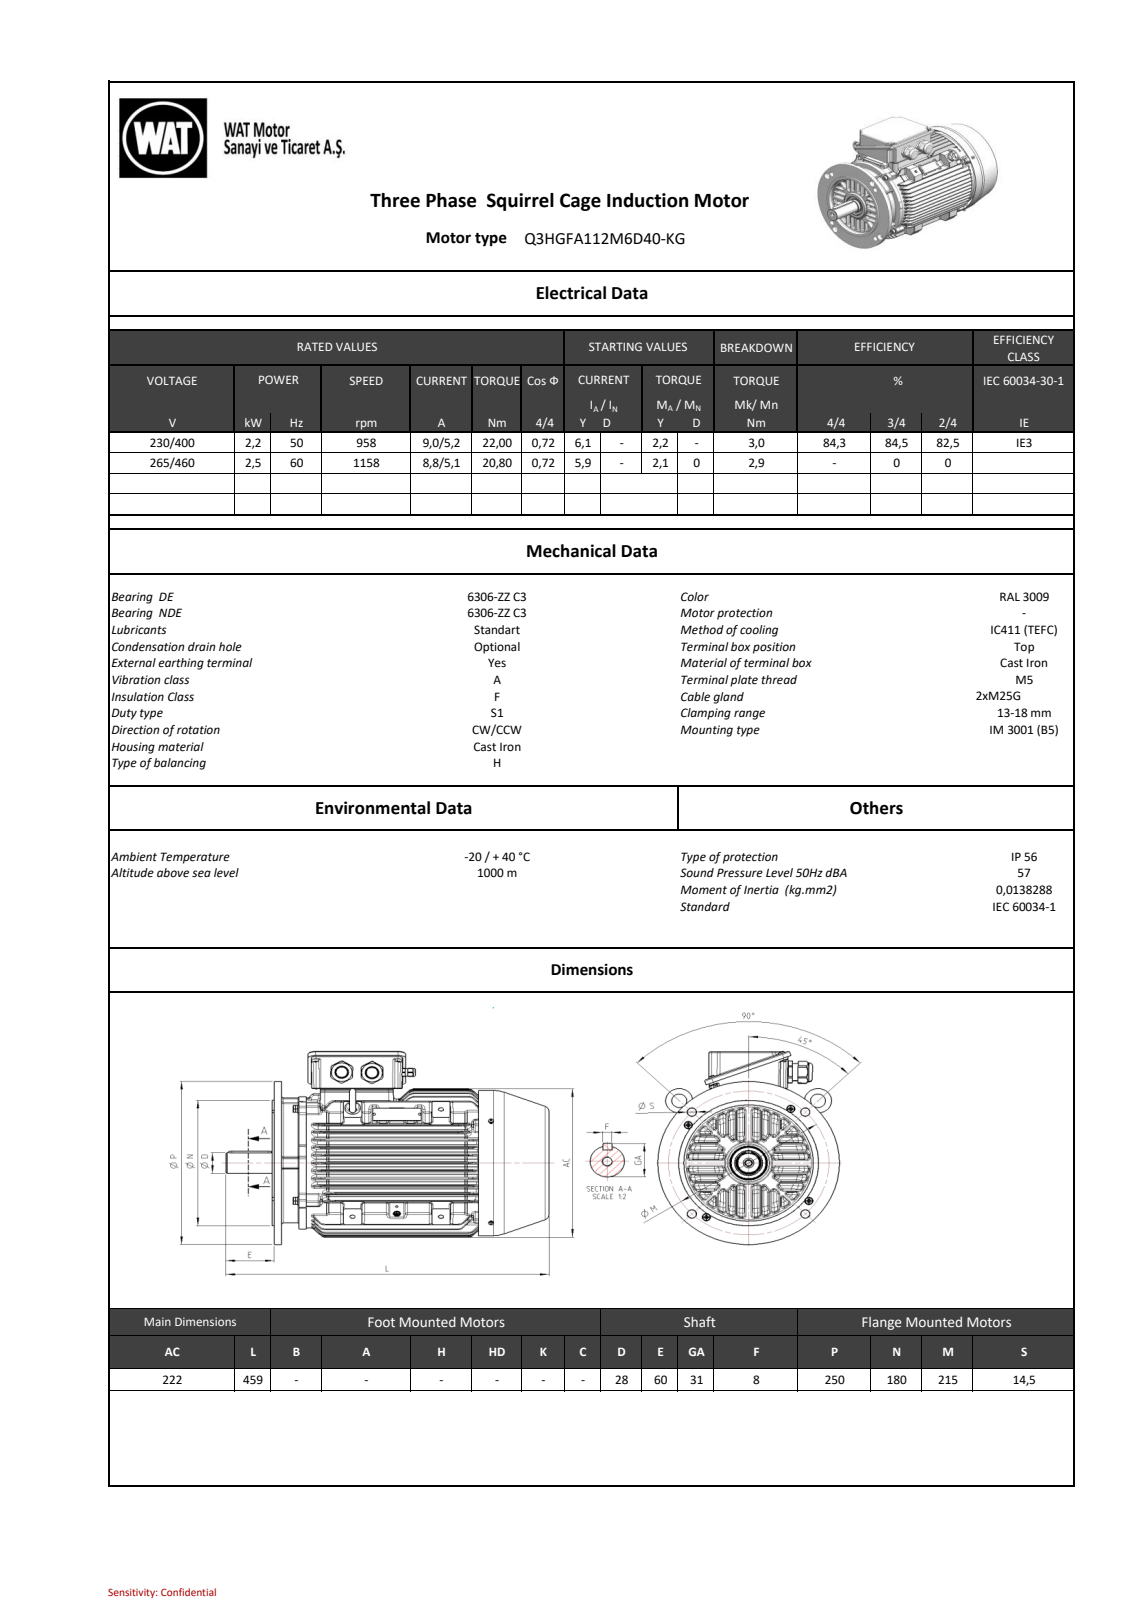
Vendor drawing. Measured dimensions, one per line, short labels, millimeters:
name: 260037F440EAov92
written by: SIEMENS PLM Software NX 11.0 (AUTOMOTIVE_DESIGN)
unit: mm
bodies: 0 solids, 4334 faces (823 planar, 1259 cylindrical, 2252 other)
size: 458.5 × 302.89 × 250
holes: 10× ⌀5, 6× ⌀4.5, 6× ⌀6.8, 4× ⌀10, 4× ⌀13, 2× ⌀2.5, 2× ⌀3.3, 2× ⌀7, 2× ⌀17.2, 1× ⌀3.5, 1× ⌀8, 1× ⌀10.5
bosses: 2× ⌀27.7, 2× ⌀25.25, 2× ⌀20, 2× ⌀12, 1× ⌀250, 1× ⌀215, 1× ⌀192, 1× ⌀180
rounds: 266× R4, 114× R1.5, 113× R0.5, 97× R3, 25× R1, 25× R1.8, 23× R2, 8× R2.75
face distances: 13.1, 26.28, 13.18, 39.96, 39.54, 26.44, 13.26, 90.54, 52.86, 39.76
hole spacings: 65.3, 97, 115, 137.18, 33.69, 38.02, 102.64, 111.28
